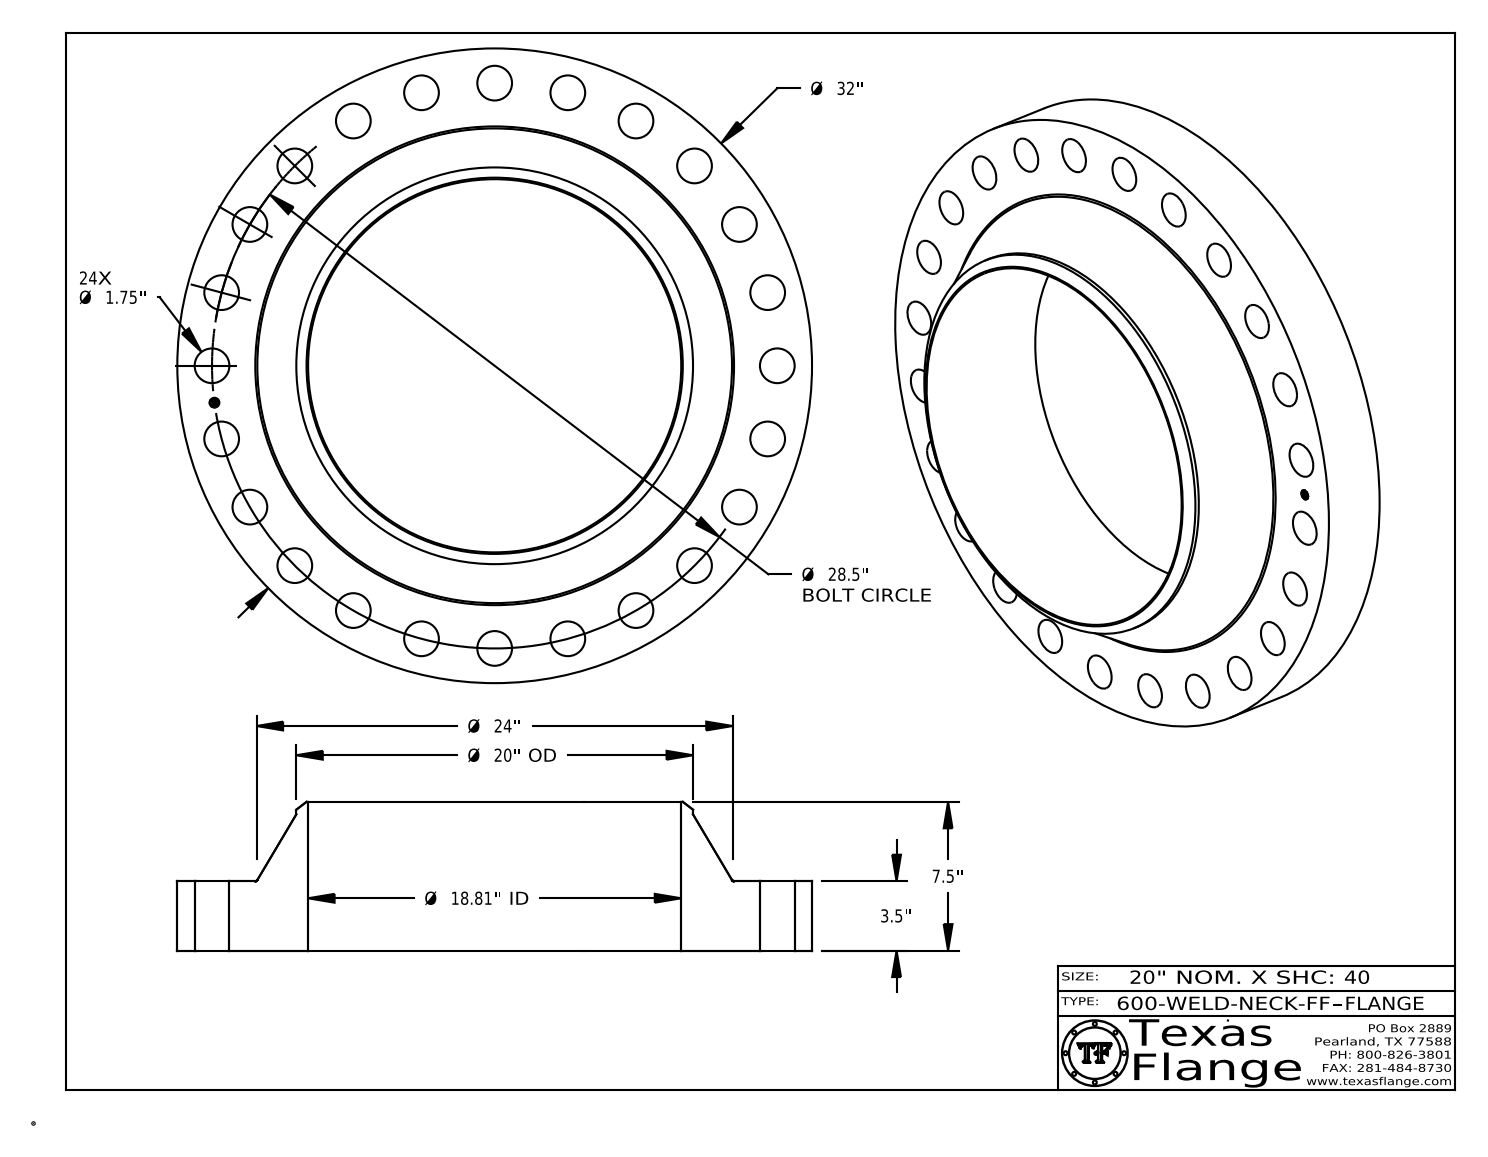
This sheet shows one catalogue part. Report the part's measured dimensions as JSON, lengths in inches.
{"part_name": "600-WELD-NECK-FF", "step_written_by": "CATIA V5 STEP AP214 (AUTOMOTIVE_DESIGN)", "units": "inches", "bodies": {"solids": 1, "faces": 448, "planar": 368, "cylindrical": 74, "other": 6}, "overall_size": [32, 32, 7.5], "volume_in3": 2004, "surface_area_in2": 2349, "round_holes": [[1.75, 24], [0.495, 1], [18.812, 1]], "round_bosses_or_shafts": [[0.03, 8], [32, 1], [20, 1], [0.39, 1]], "face_to_face_distances": [3.5, 7.5, 4, 0.015, 3.485, 4.015, 0.148, 0.145, 0.027, 0.096], "hole_center_spacings": [14.25, 3.72, 7.376, 24.682, 26.331, 27.529, 20.153, 10.907]}
